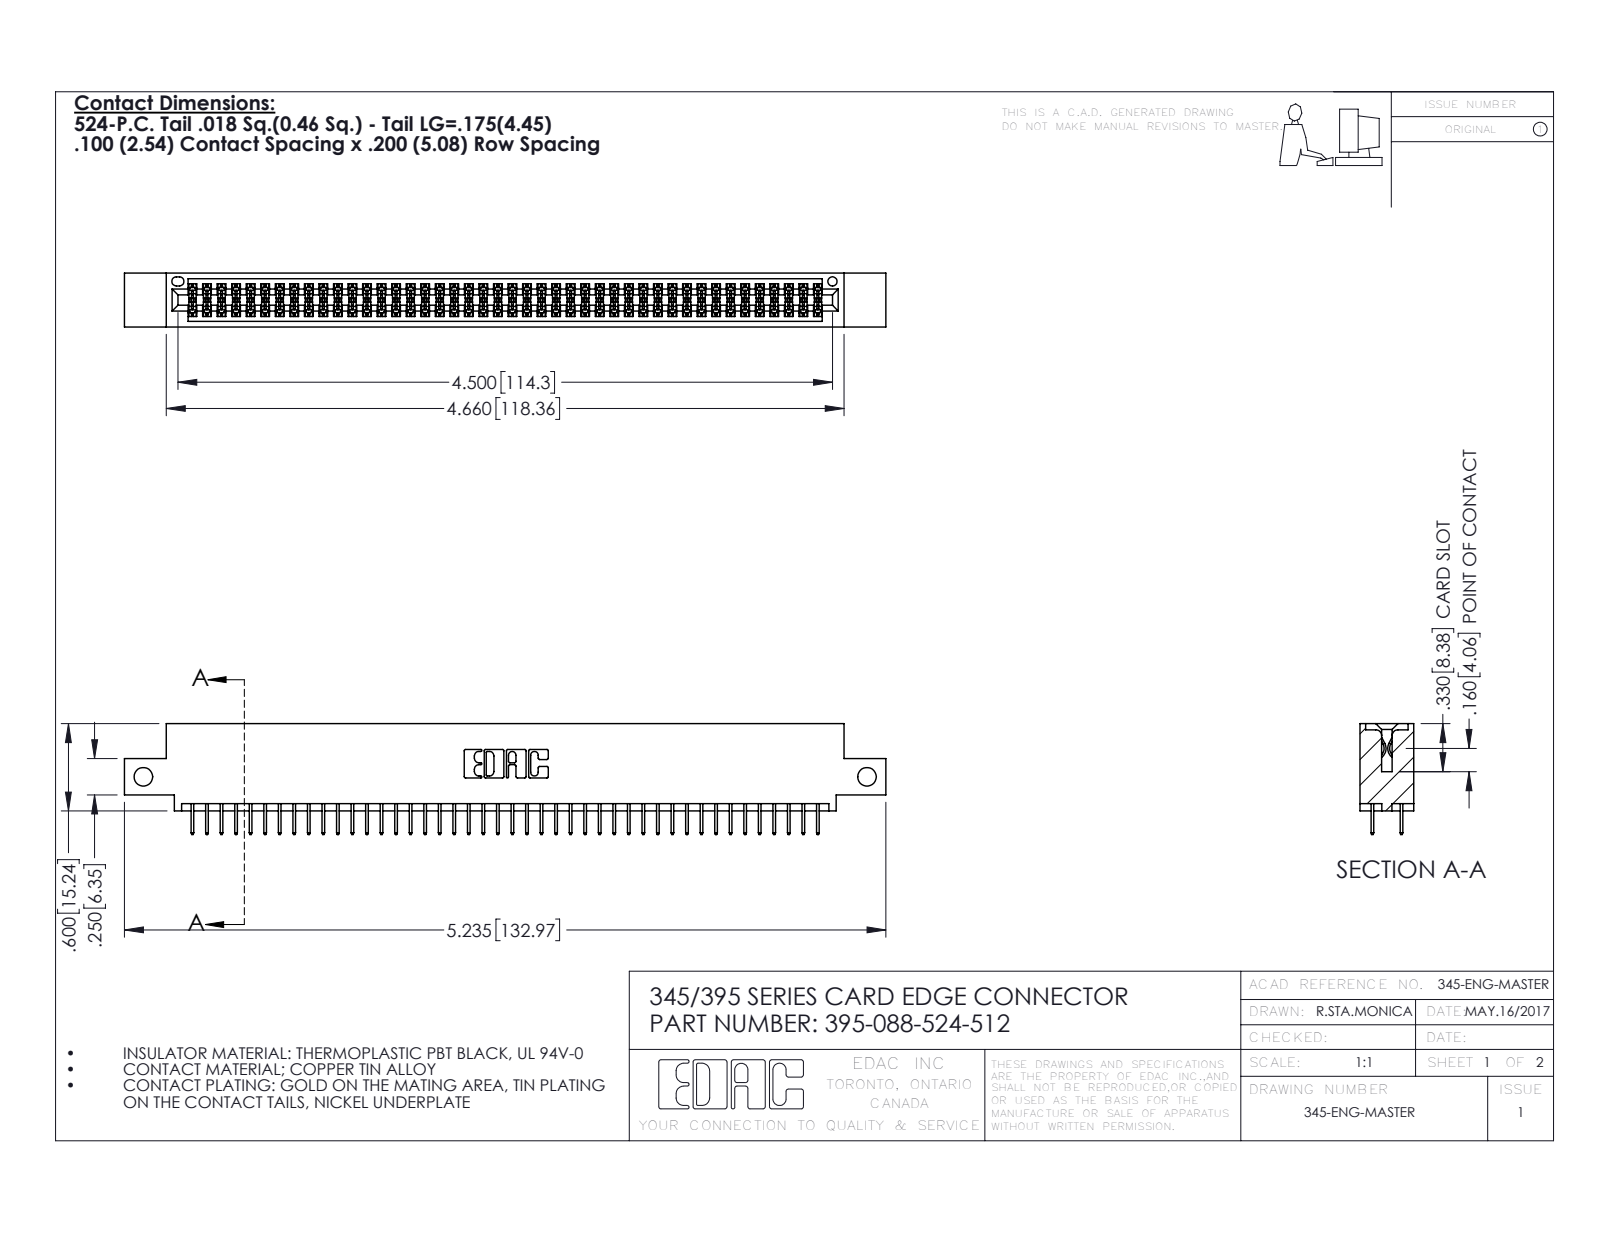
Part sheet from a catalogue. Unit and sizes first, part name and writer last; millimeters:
Units: millimetres
Overall size (bounding box): 133 × 19.4 × 9.4
Round holes (diameter × count): ⌀3.3 ×2, ⌀1.6 ×1
Partial cylindrical surfaces — rounded edges, fillets, slot ends (radius × count): R0.2 ×132, R0.3 ×22, R0.2 ×6, R0.8 ×6, R0.7 ×3, R0.4 ×2, R0.5 ×2, R0.6 ×2
Main face-to-face distances: 1.8, 7.6, 5.1, 9.4, 2.5, 6.9, 0.6, 5.7, 1.8, 4.4
Hole centre spacings: 126.4
Volume: 12 600 mm³ · Surface area: 18 330 mm²
Bodies: 89 solids, 4882 faces (3516 planar, 1366 cylindrical, 0 other)
Part name (STEP PRODUCT): 345 Part_0.110 Offset - Side Mount; 345-292-001_345-293-124; 395-088-524-512
STEP written by: SolidWorks 2016 (CONFIG_CONTROL_DESIGN)
